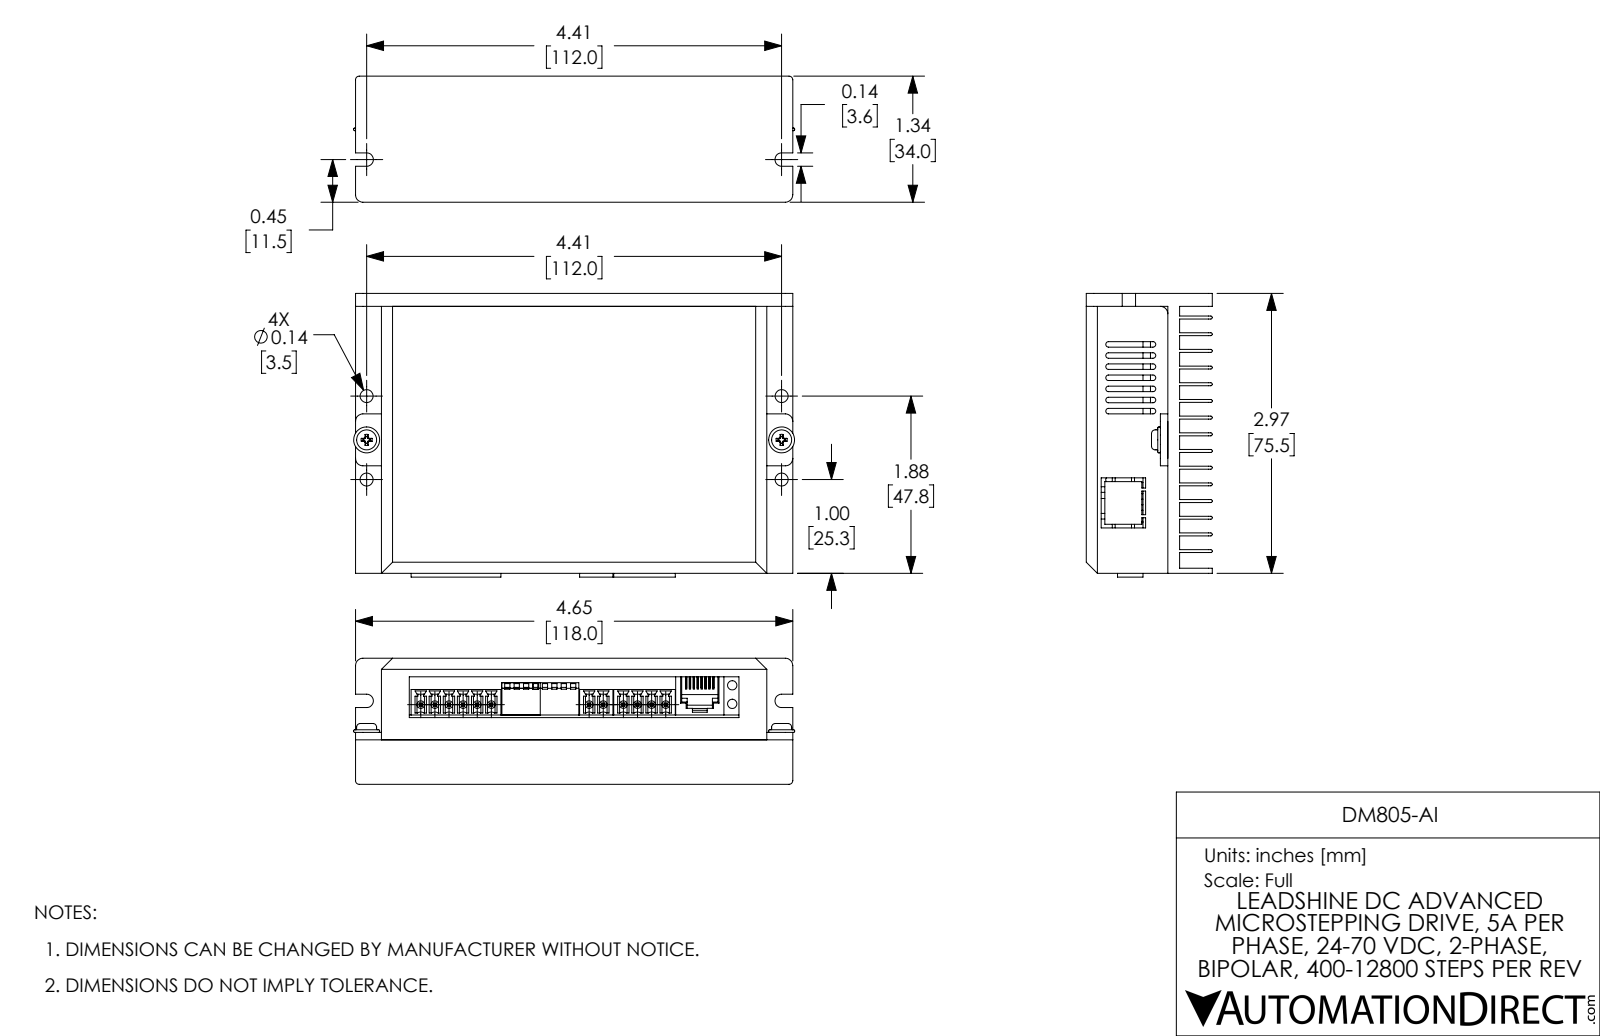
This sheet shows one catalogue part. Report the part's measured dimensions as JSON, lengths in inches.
{"part_name": "DM805-AI_3D", "step_written_by": "SolidWorks 2017 (AUTOMOTIVE_DESIGN)", "units": "inches", "bodies": {"solids": 17, "faces": 1450, "planar": 1066, "cylindrical": 315, "other": 69}, "overall_size": [4.685, 3.012, 1.339], "volume_in3": 5.744, "surface_area_in2": 163.9, "round_holes": [[0.03, 8], [0.138, 6]], "round_bosses_or_shafts": [[0.012, 16], [0.08, 12], [0.276, 2], [0.213, 2], [0.118, 2], [0.098, 2], [0.093, 2], [0.016, 2]], "partial_cylinders_radius": [[0.03, 28], [0.016, 15], [0.06, 12], [0.079, 7], [0.039, 2], [0.071, 2], [0.273, 1], [0.307, 1]], "face_to_face_distances": [0.079, 0.602, 0.177, 0.354, 0.531, 0.886, 0.311, 0.264, 0.709, 0.866], "hole_center_spacings": [0.038, 0.076, 0.113, 4.409, 0.038, 0.04, 0.078, 0.115]}
